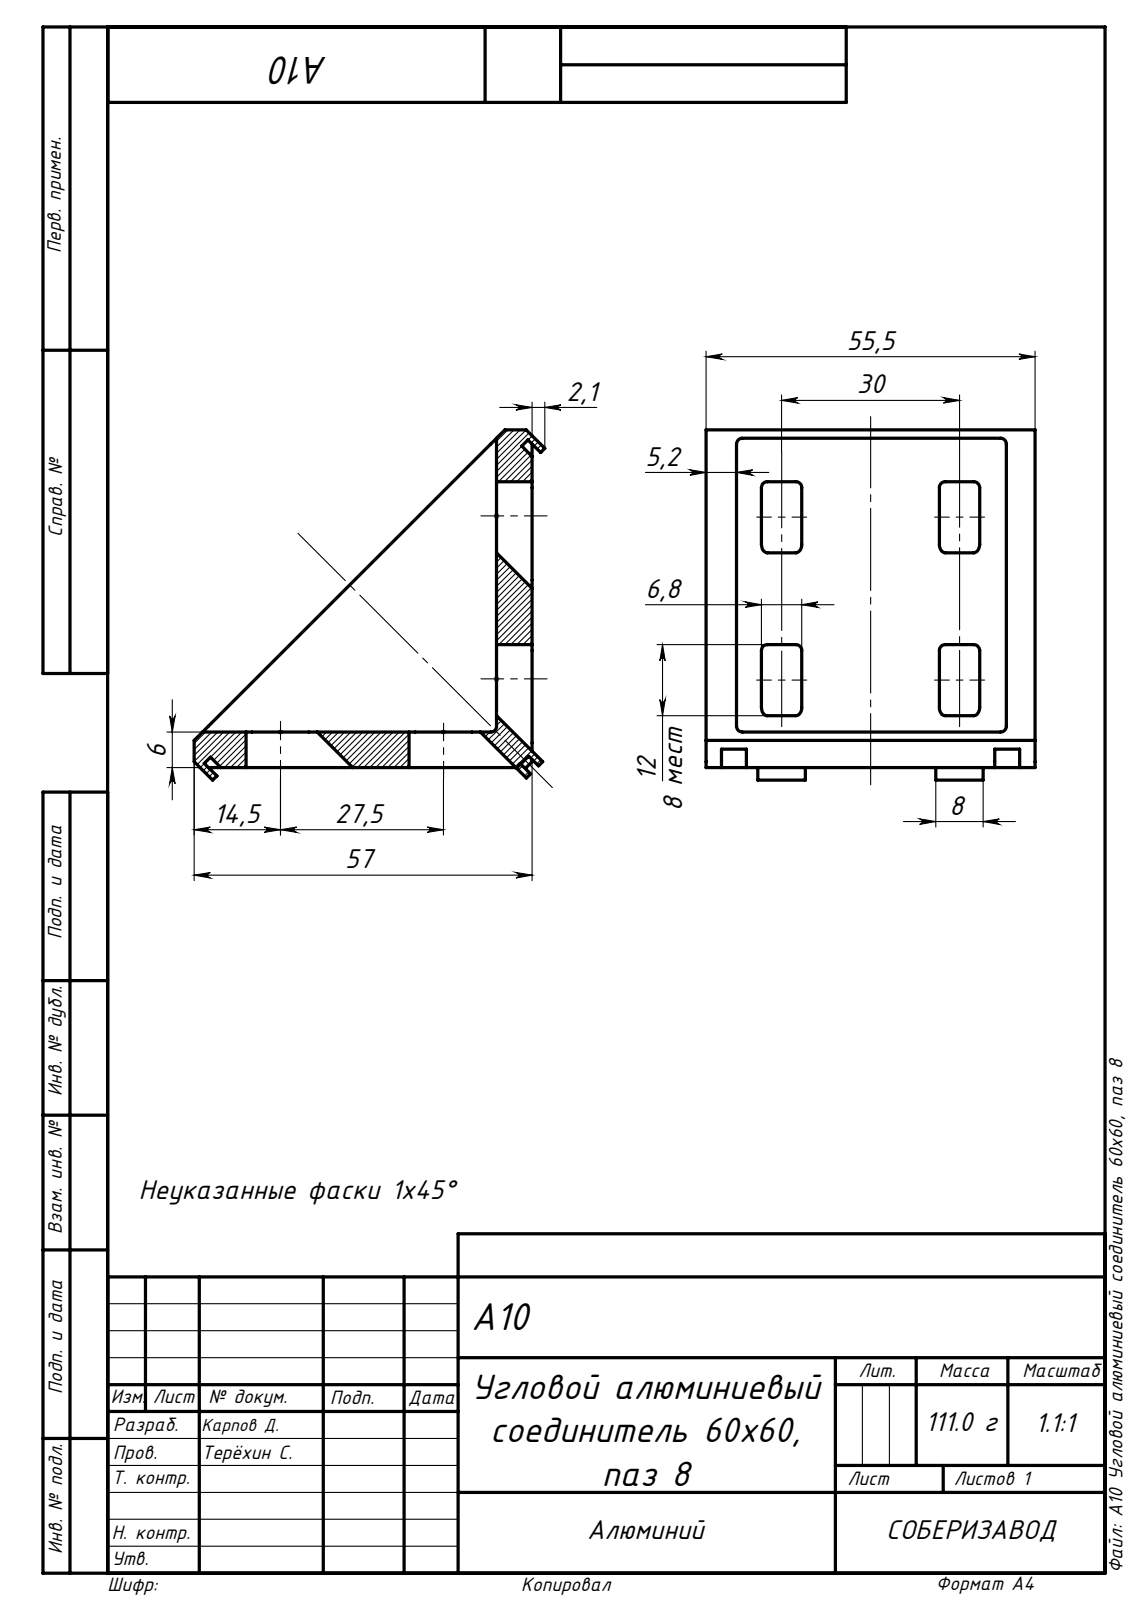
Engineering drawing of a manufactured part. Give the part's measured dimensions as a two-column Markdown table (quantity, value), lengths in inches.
| quantity | value |
| --- | --- |
| part name | A10 Угловой алюминиевый соединитель 60х60, паз 8 |
| STEP written by | SolidWorks 2021 (AUTOMOTIVE_DESIGN) |
| units | inches |
| bodies | 3 solids, 205 faces (166 planar, 37 cylindrical, 2 other) |
| overall size | 2.328 × 2.328 × 2.185 |
| volume | 2.409 in³ |
| surface area | 32.86 in² |
| partial cylindrical surfaces (radius × count) | 0.039 × 37 |
| main face-to-face distances | 0.236, 2.185, 0.102, 0.134, 0.203, 1.982, 1.994, 1.791, 0.191, 0.268 |
